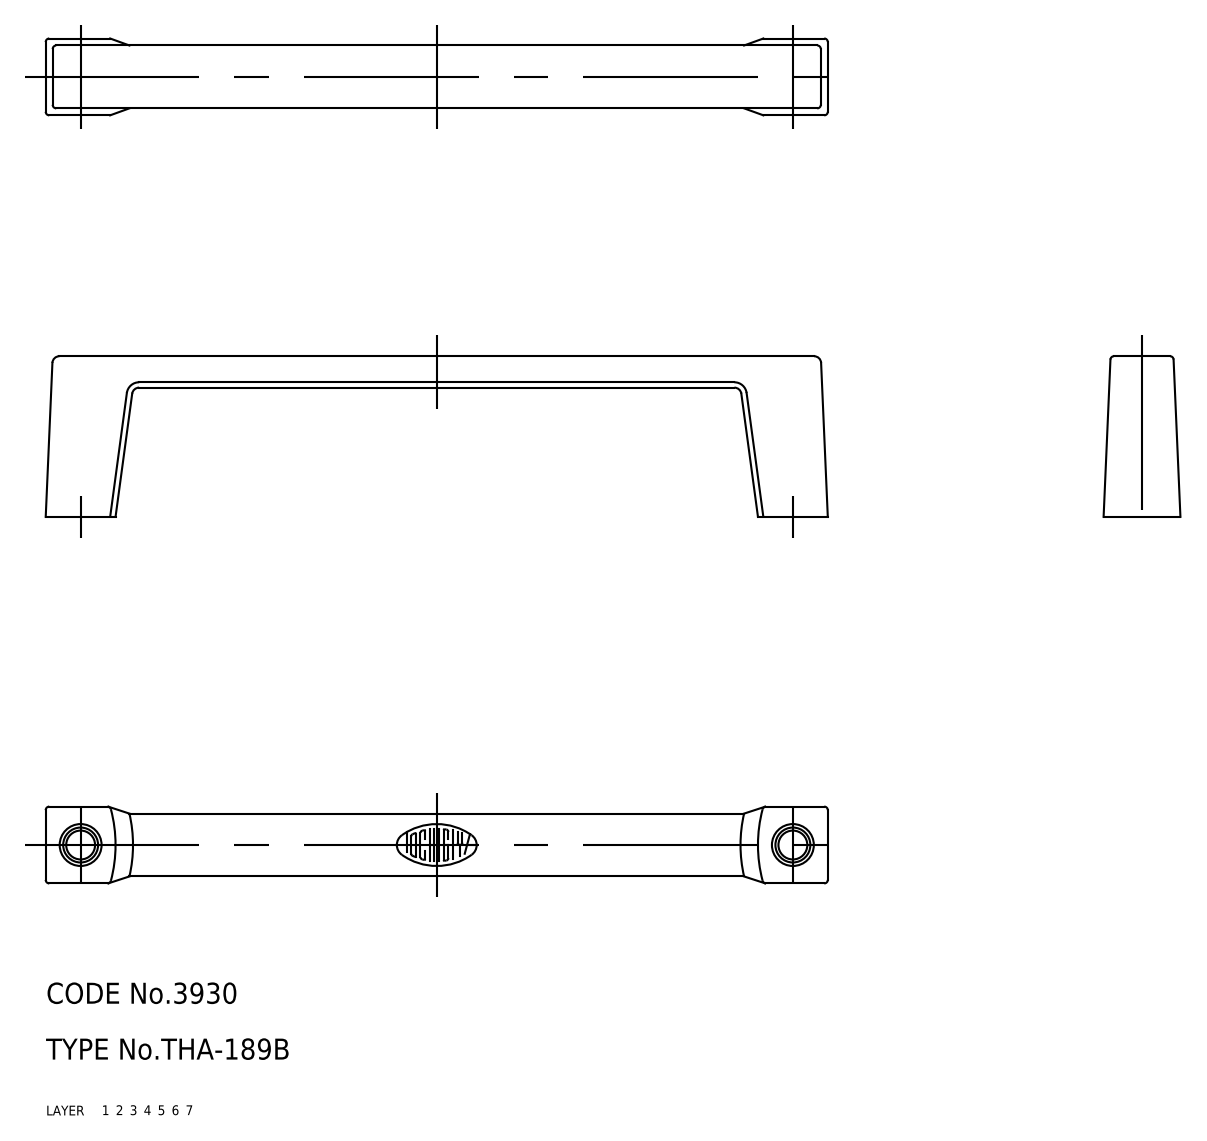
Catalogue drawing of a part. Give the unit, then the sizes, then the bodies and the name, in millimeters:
Units: millimetres
Overall size (bounding box): 112 × 23 × 11
Volume: 7 992 mm³ · Surface area: 4 732 mm²
Bodies: 1 solid, 40 faces (0 planar, 0 cylindrical, 40 other)
Part name (STEP PRODUCT): pull
STEP written by: CADfix (AUTOMOTIVE_DESIGN)
